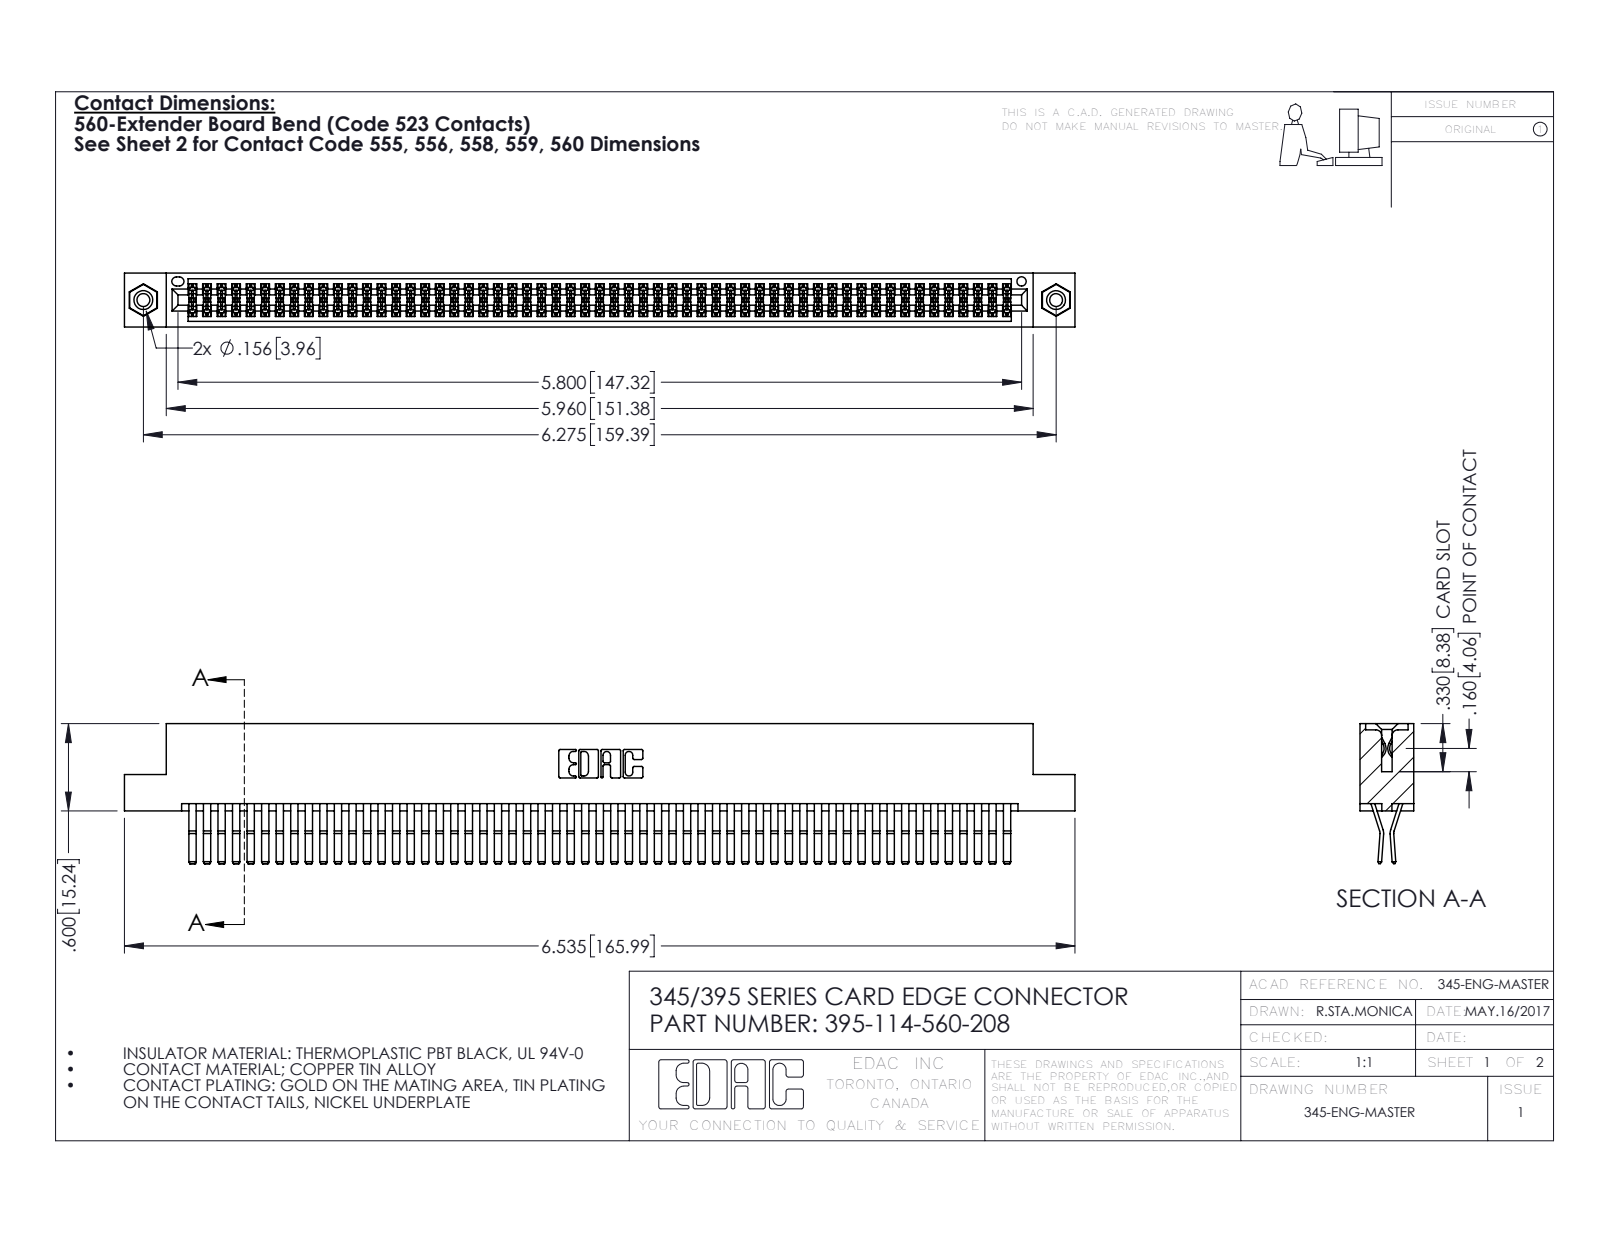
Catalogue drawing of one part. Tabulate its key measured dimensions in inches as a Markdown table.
| quantity | value |
| --- | --- |
| part name | 345 Part_Flush Mounting Lugs - 0.156 Dia-TI; 395-114-560-208; 345-250-001_345-250-003-102; 345-292-001_560 Tail |
| STEP written by | SolidWorks 2016 (CONFIG_CONTROL_DESIGN) |
| units | inches |
| bodies | 117 solids, 6114 faces (3874 planar, 2224 cylindrical, 16 other) |
| overall size | 6.535 × 0.962 × 0.37 |
| volume | 1.038 in³ |
| surface area | 42.41 in² |
| round holes (diameter × count) | 0.089 × 2, 0.125 × 2, 0.156 × 2, 0.064 × 1 |
| round bosses / shafts (diameter × count) | 0.155 × 2 |
| partial cylindrical surfaces (radius × count) | 0.006 × 171, 0.01 × 22, 0.007 × 6, 0.031 × 6, 0.026 × 3, 0.01 × 2, 0.014 × 2, 0.019 × 2 |
| main face-to-face distances | 0.025, 0.072, 0.298, 0.37, 0.2, 0.098, 0.272, 0.225, 0.175, 0.149 |
| hole center spacings | 0.27, 6.039, 6.275 |
